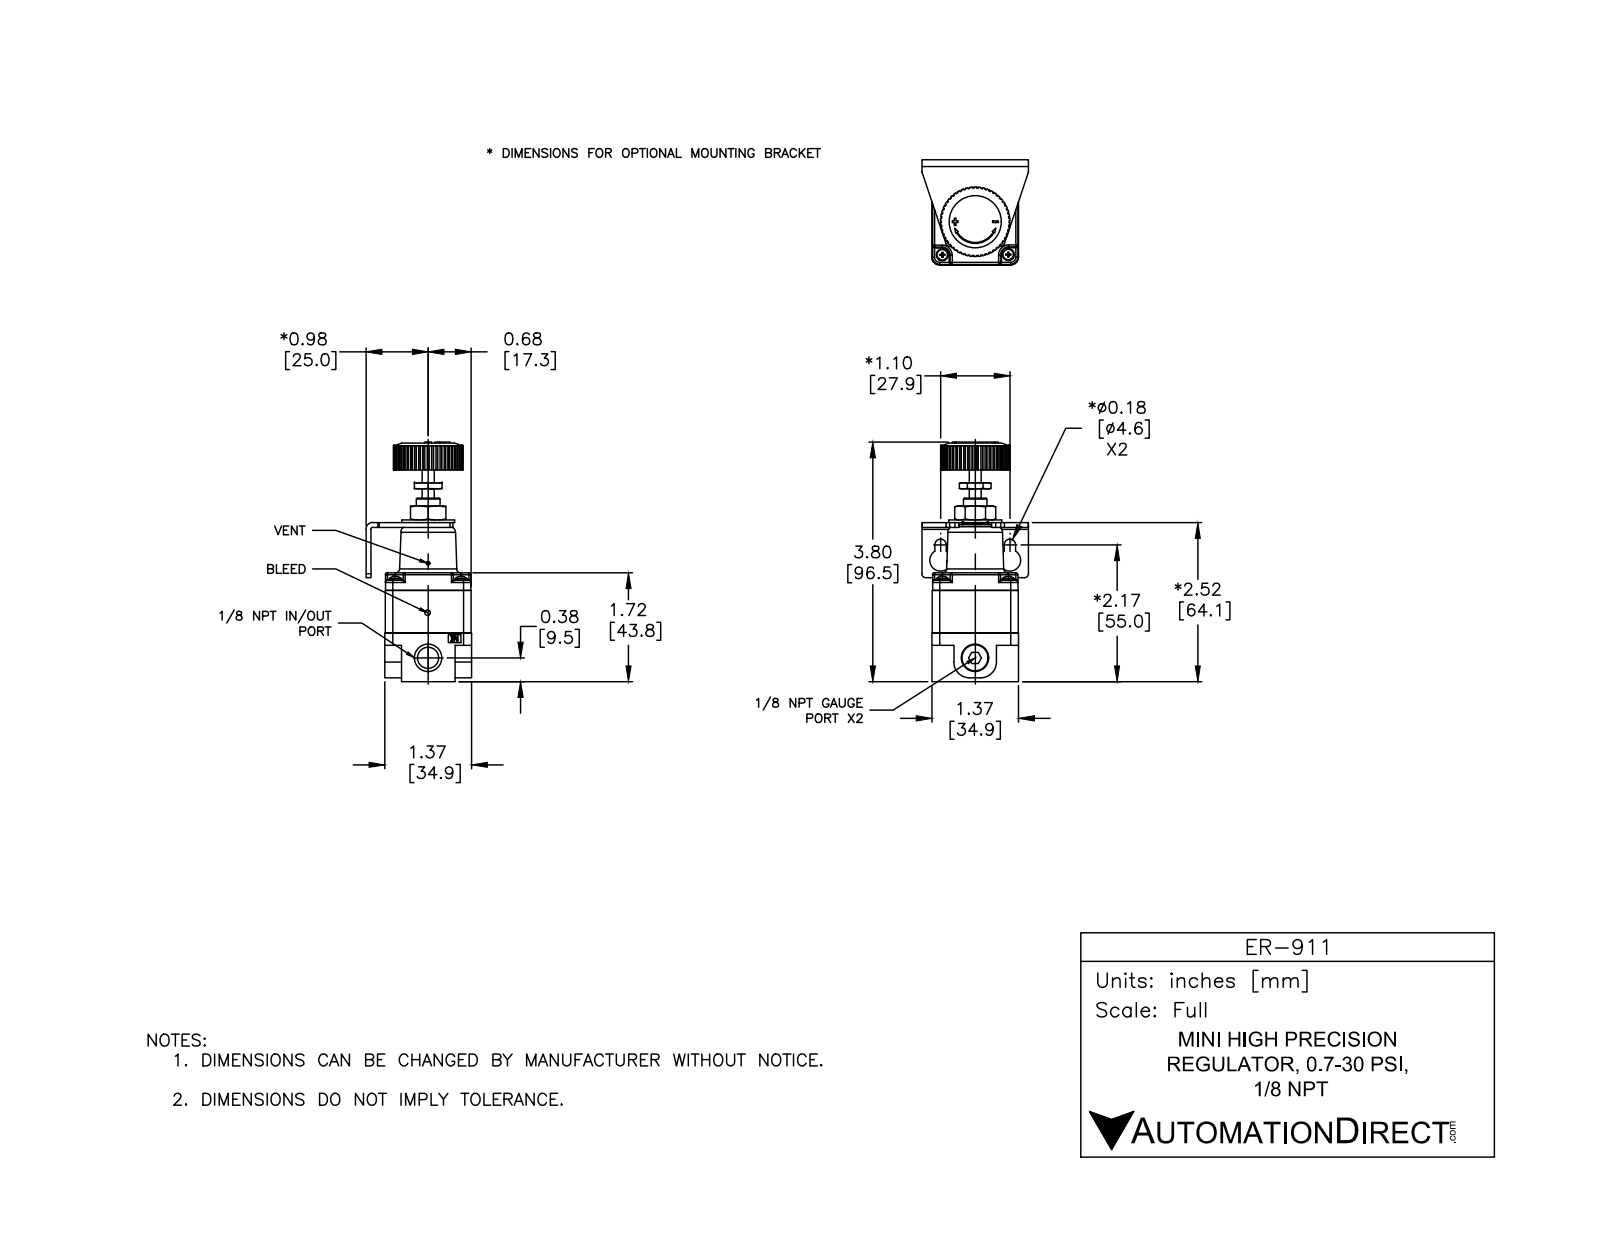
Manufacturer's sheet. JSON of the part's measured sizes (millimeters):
{"part_name": "ER-911", "step_written_by": "SolidWorks 2015 (CONFIG_CONTROL_DESIGN)", "units": "millimeters", "bodies": {"solids": 16, "faces": 764, "planar": 446, "cylindrical": 201, "other": 117}, "overall_size": [96.2, 34.9, 34.9], "volume_mm3": 56810, "surface_area_mm2": 18860, "round_holes": [[5.1, 4], [8.4, 3], [1.6, 2], [3.4, 2], [7.4, 2], [3.3, 1], [9.7, 1], [10.4, 1], [23.9, 1]], "round_bosses_or_shafts": [[4.7, 4], [4.3, 4], [2.6, 4], [21.3, 1], [10.5, 1], [10.2, 1], [9.5, 1], [7.6, 1]], "partial_cylinders_radius": [[0.8, 24], [2.2, 4], [2.4, 4], [2.5, 4], [3.2, 4], [6.4, 2], [7.5, 1], [9.1, 1]], "face_to_face_distances": [34.6, 34.8, 6.5, 28.1, 34.5, 34.9, 6.7, 28.2, 61.8, 93.8], "hole_center_spacings": [7.3, 10.2, 20.5, 5.8, 8.2, 11.6, 12.7, 15.3]}
